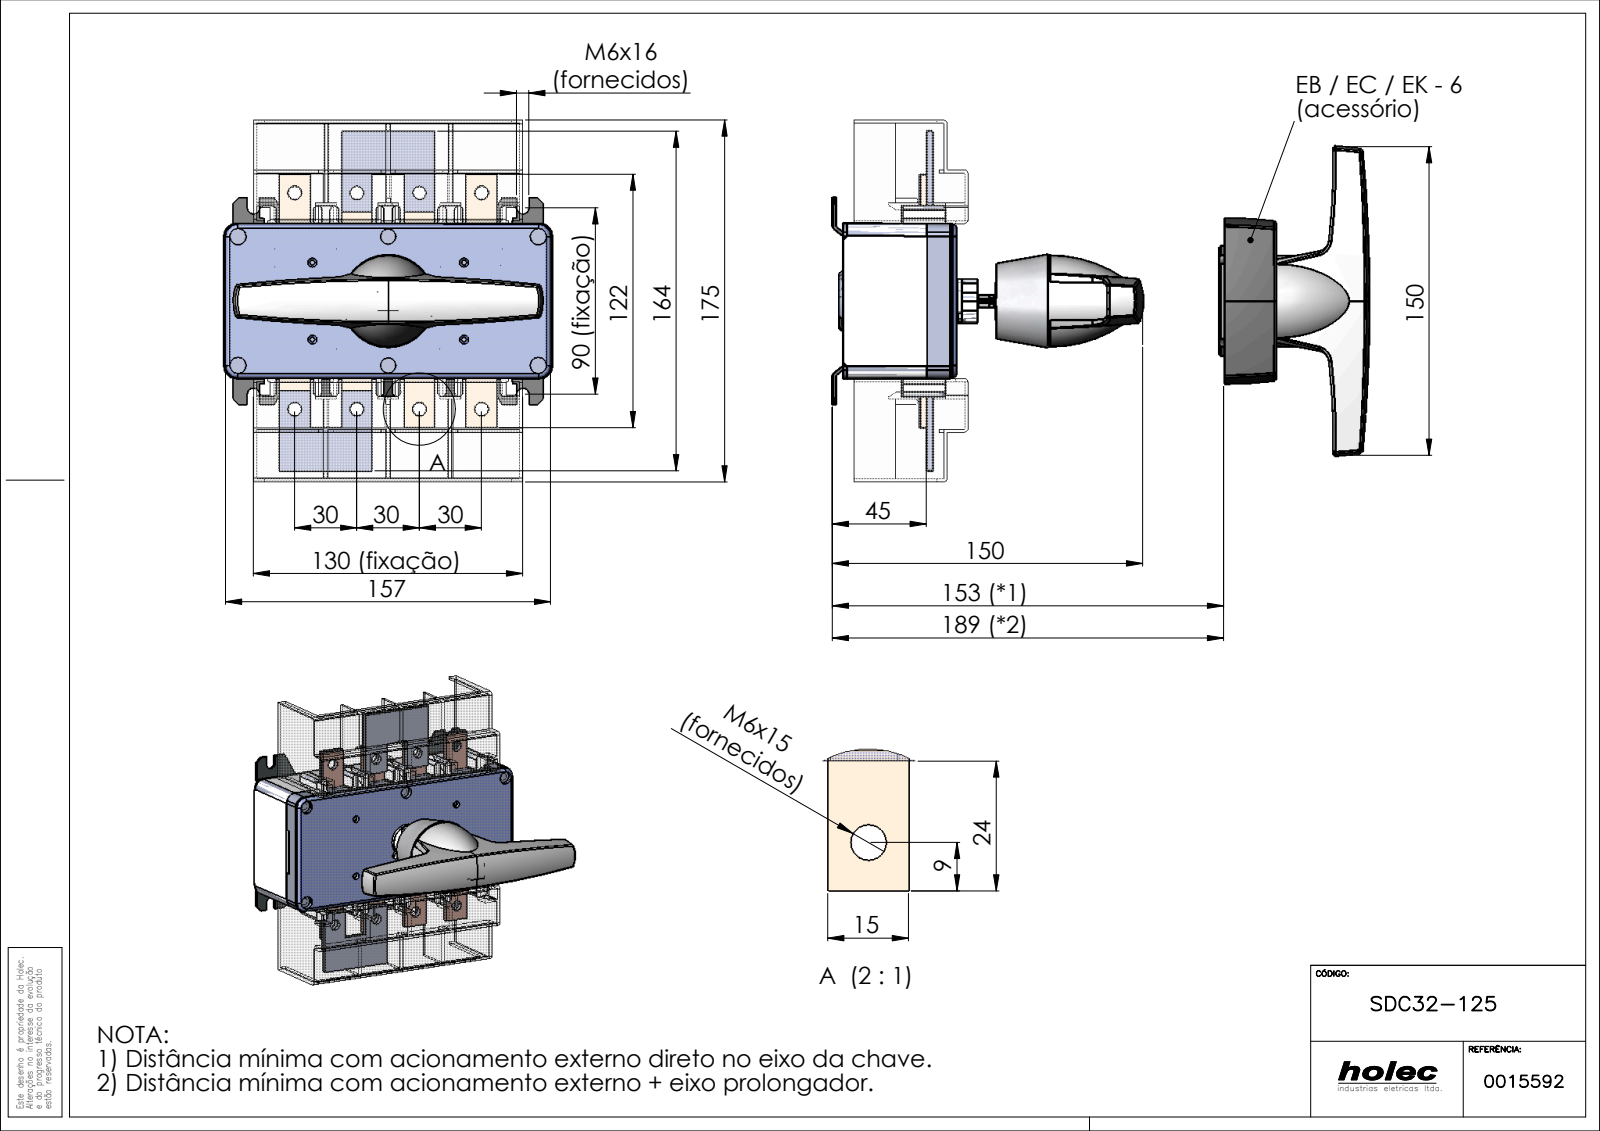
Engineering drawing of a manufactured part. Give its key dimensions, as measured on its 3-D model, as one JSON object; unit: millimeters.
{"part_name": "SDC32-125; SDC32-125-1; Q-152", "step_written_by": "SolidWorks 2017 (CONFIG_CONTROL_DESIGN)", "units": "millimeters", "bodies": {"solids": 5, "faces": 1061, "planar": 685, "cylindrical": 236, "other": 140}, "overall_size": [174.72, 158.7, 150.2], "volume_mm3": 807274, "surface_area_mm2": 211179, "round_holes": [[6.6, 8], [2.4, 4], [8, 4], [6.75, 2], [7.5, 2], [3.5, 1], [6.2, 1], [6.38, 1], [12.2, 1], [24.2, 1], [39, 1]], "round_bosses_or_shafts": [[44, 1], [28.2, 1], [24.5, 1], [22, 1], [21, 1], [15.5, 1], [12, 1]], "partial_cylinders_radius": [[2, 32], [0.5, 10], [6, 10], [4.5, 7], [1.5, 4], [3, 4], [3.1, 4], [587.86, 4]], "face_to_face_distances": [1.5, 1.3, 10, 5.9, 4.1, 51.8, 54.9, 3.1, 30, 53.1], "hole_center_spacings": [25.95, 30, 34.58, 34.66, 38.01, 38.68, 39.89, 41.06]}
